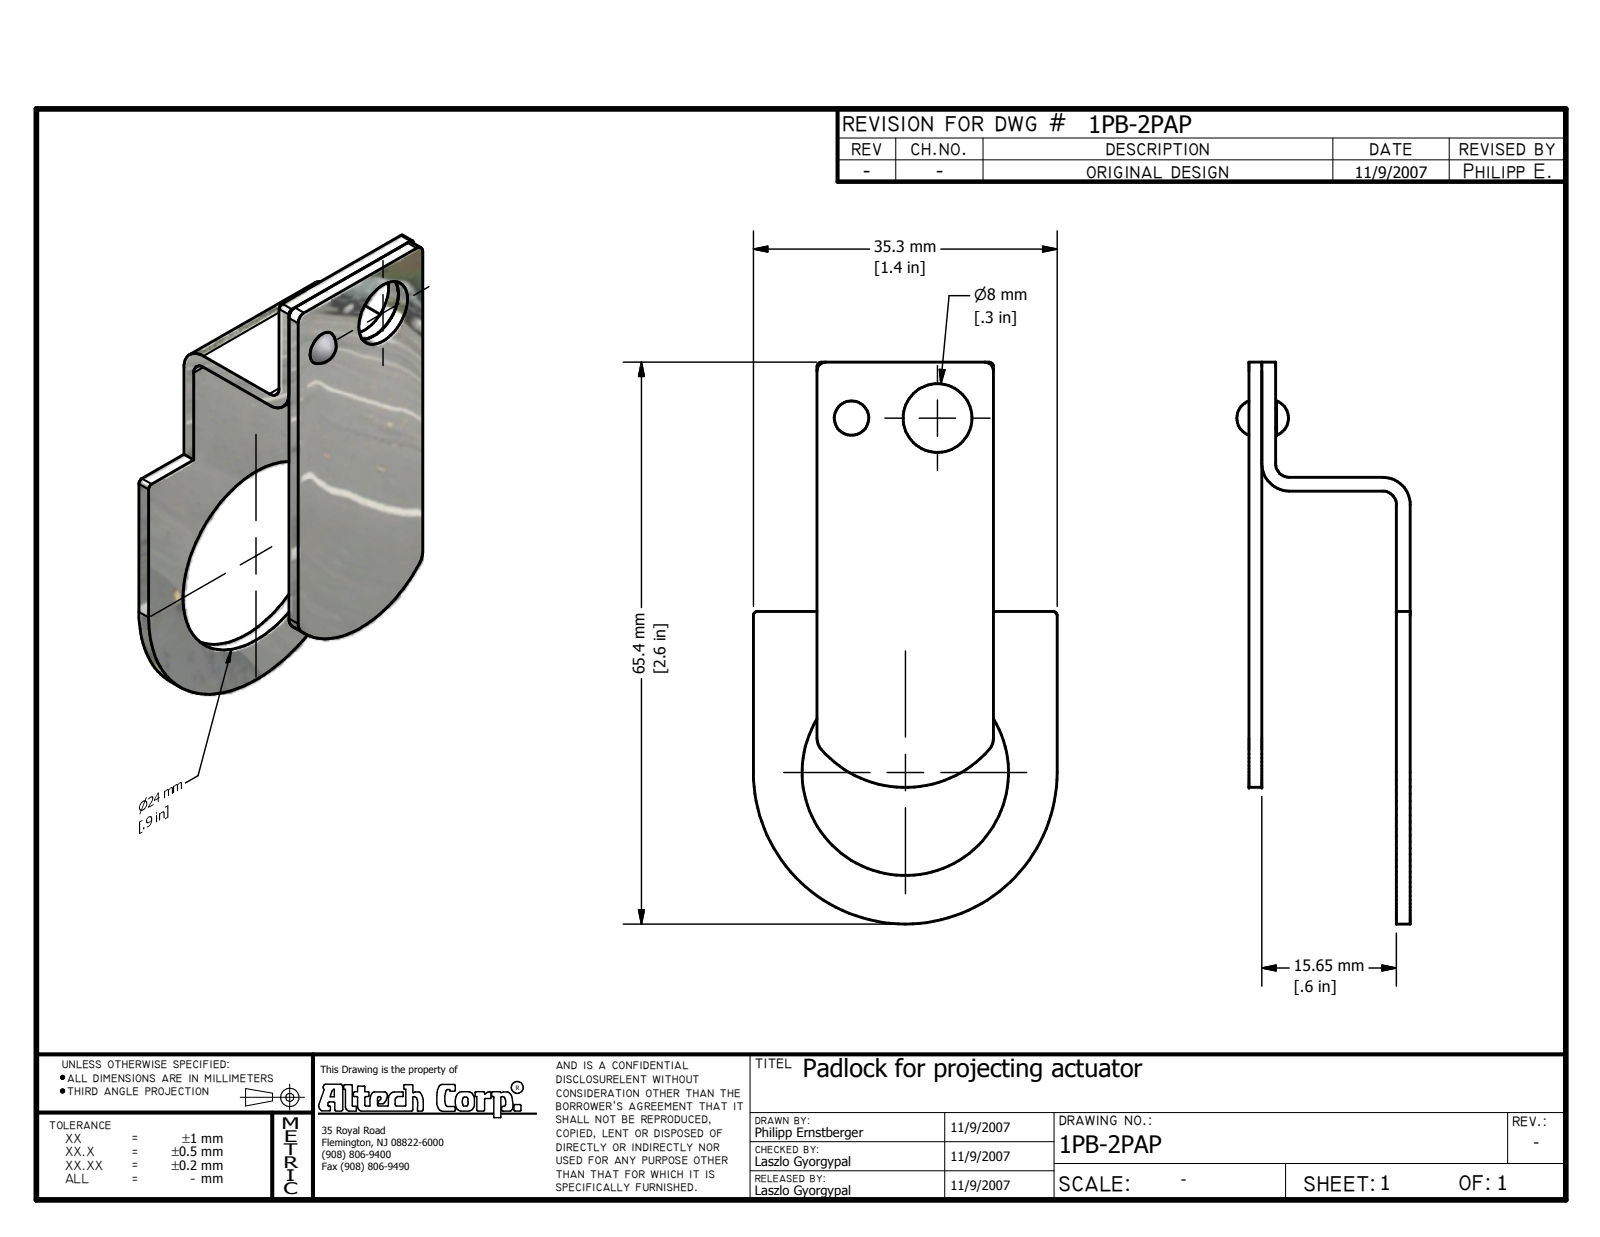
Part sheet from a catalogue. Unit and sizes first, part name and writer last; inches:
Units: inches
Overall size (bounding box): 2.575 × 1.39 × 0.793
Round holes (diameter × count): ⌀0.098 ×1, ⌀0.315 ×1, ⌀0.945 ×1
Round bosses / shafts (diameter × count): ⌀0.091 ×1
Partial cylindrical surfaces — rounded edges, fillets, slot ends (radius × count): R0.02 ×4, R0.039 ×2, R0.063 ×2, R0.079 ×2, R0.126 ×2, R0.512 ×1, R0.695 ×1
Main face-to-face distances: 0.063, 0.616, 0.679, 0.738, 0.675, 0.059, 0.553, 0.122, 0.807, 0.591
Hole centre spacings: 0.394, 1.631, 1.643
Volume: 0.235 in³ · Surface area: 8.878 in²
Bodies: 3 solids, 42 faces (20 planar, 20 cylindrical, 2 other)
Part name (STEP PRODUCT): 2PAP; standoff; top; SS 1440 - KN 2.3 x 18 x 3
STEP written by: Autodesk Inventor 2008 (AUTOMOTIVE_DESIGN)
